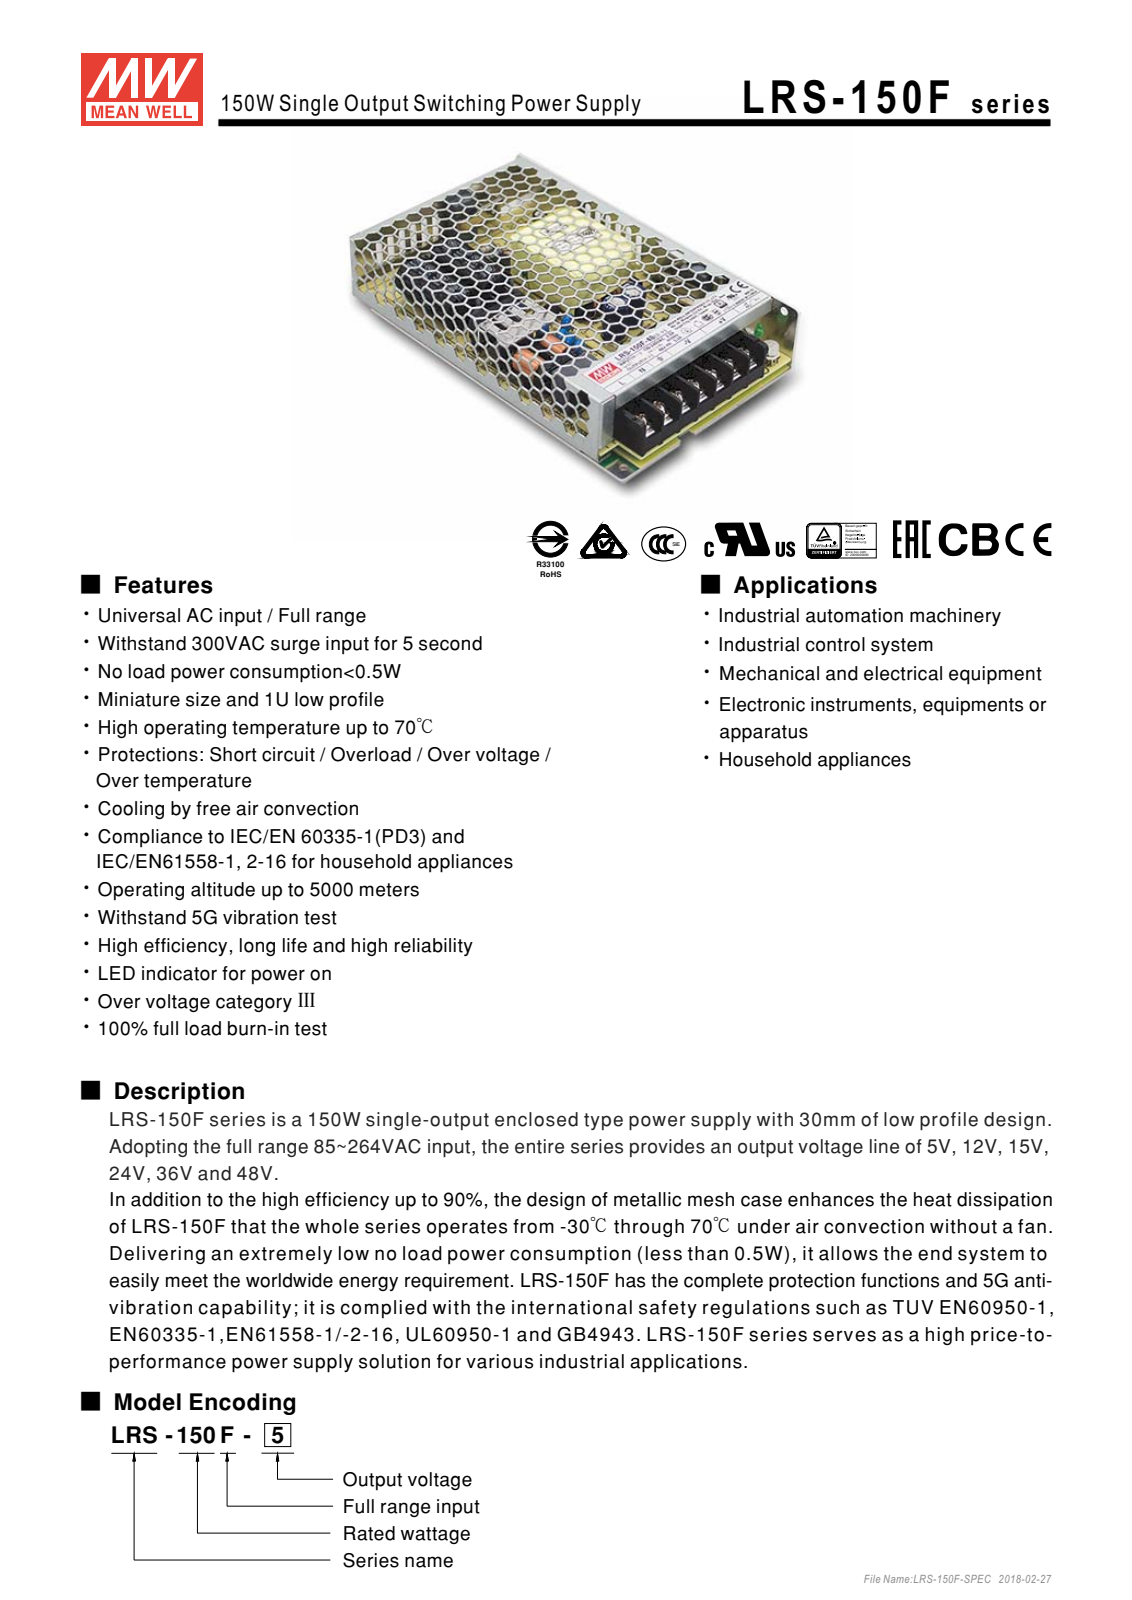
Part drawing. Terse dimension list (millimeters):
name: BASE_2; BASE_3; BASE_4; BASE_5 (+8 more)
written by: Alibre (AUTOMOTIVE_DESIGN)
unit: mm
bodies: 52 solids, 6523 faces (5716 planar, 220 cylindrical, 587 other)
size: 300.8 × 189.2 × 31.4
volume: 131 700 mm³; area: 171 900 mm²
holes: 9× ⌀2.5, 7× ⌀3.2, 7× ⌀3.8, 3× ⌀1.9, 3× ⌀3.5, 3× ⌀3.9, 2× ⌀1.2, 1× ⌀3, 1× ⌀3.4, 1× ⌀3.5
bosses: 7× ⌀6.2, 7× ⌀3.5, 5× ⌀7.7, 3× ⌀5.3, 3× ⌀4.9, 3× ⌀3.5, 3× ⌀3, 3× ⌀2.7
rounds: 28× R1.5, 12× R0.8, 10× R0.8, 8× R1.8, 6× R0.8, 6× R0.8, 5× R2, 4× R0.9
face distances: 1.5, 0.4, 1.5, 3.2, 4.7, 6.2, 4.7, 0.8, 0.4, 0.4
hole spacings: 9.5, 19, 28.5, 9.5, 19.1, 38, 38, 5.9
